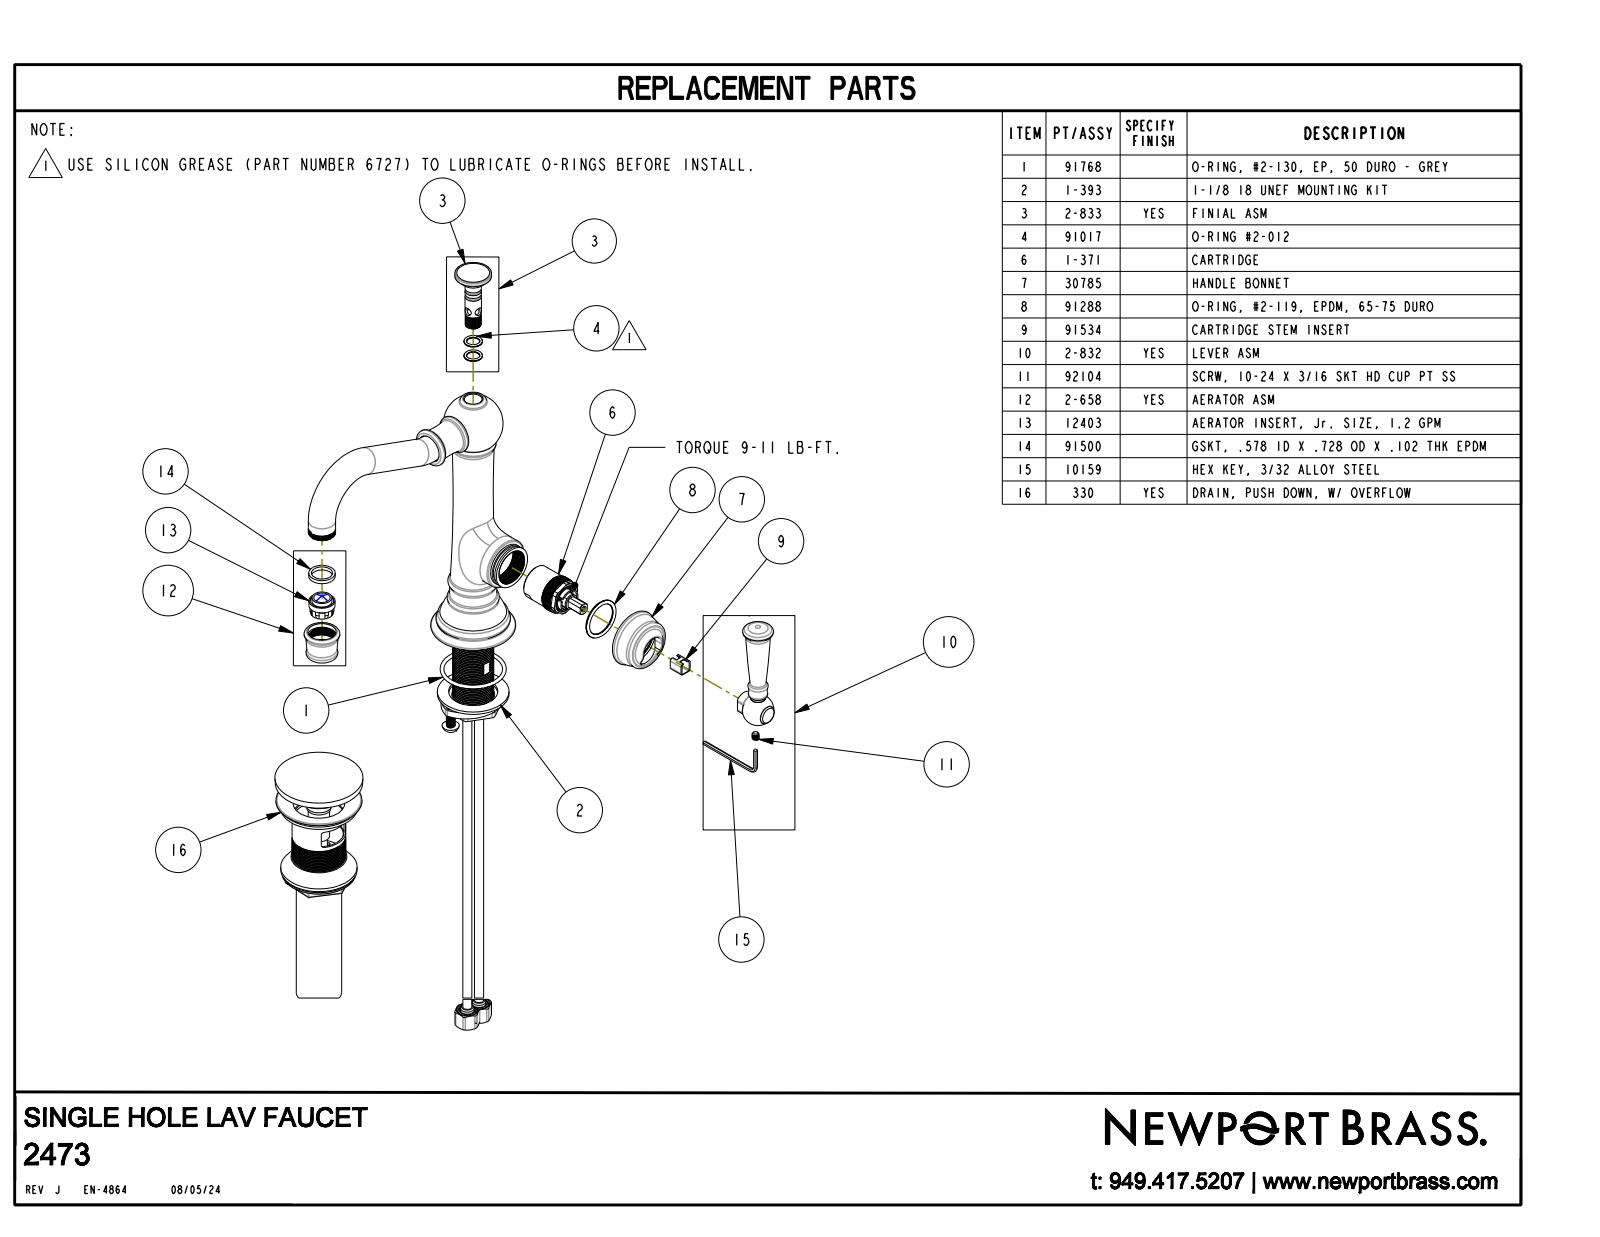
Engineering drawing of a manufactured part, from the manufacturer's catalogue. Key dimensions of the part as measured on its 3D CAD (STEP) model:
Part name (STEP PRODUCT): 2473_SW0001
STEP written by: CREO PARAMETRIC BY PTC INC, 2018400 (AUTOMOTIVE_DESIGN)
Units: inches
Bodies: 1 solid, 358 faces (54 planar, 79 cylindrical, 225 other)
Overall size (bounding box): 8.097 × 7.546 × 4.088
Volume: 17.21 in³ · Surface area: 81.1 in²
Round holes (diameter × count): ⌀0.48 ×1, ⌀0.921 ×1, ⌀1.25 ×1, ⌀1.273 ×1
Round bosses / shafts (diameter × count): ⌀0.75 ×2, ⌀1.43 ×1, ⌀1.295 ×1, ⌀1.28 ×1, ⌀1.07 ×1, ⌀1.008 ×1, ⌀0.98 ×1, ⌀0.89 ×1
Partial cylindrical surfaces — rounded edges, fillets, slot ends (radius × count): R0.1 ×12, R0.06 ×4, R0.353 ×3, R0.094 ×2, R0.313 ×2, R3.64 ×2, R0.09 ×1, R0.31 ×1
Main face-to-face distances: 0.388, 5.597, 0.08, 0.468, 0.138, 0.526, 0.606, 0.595, 6.142, 0.545
